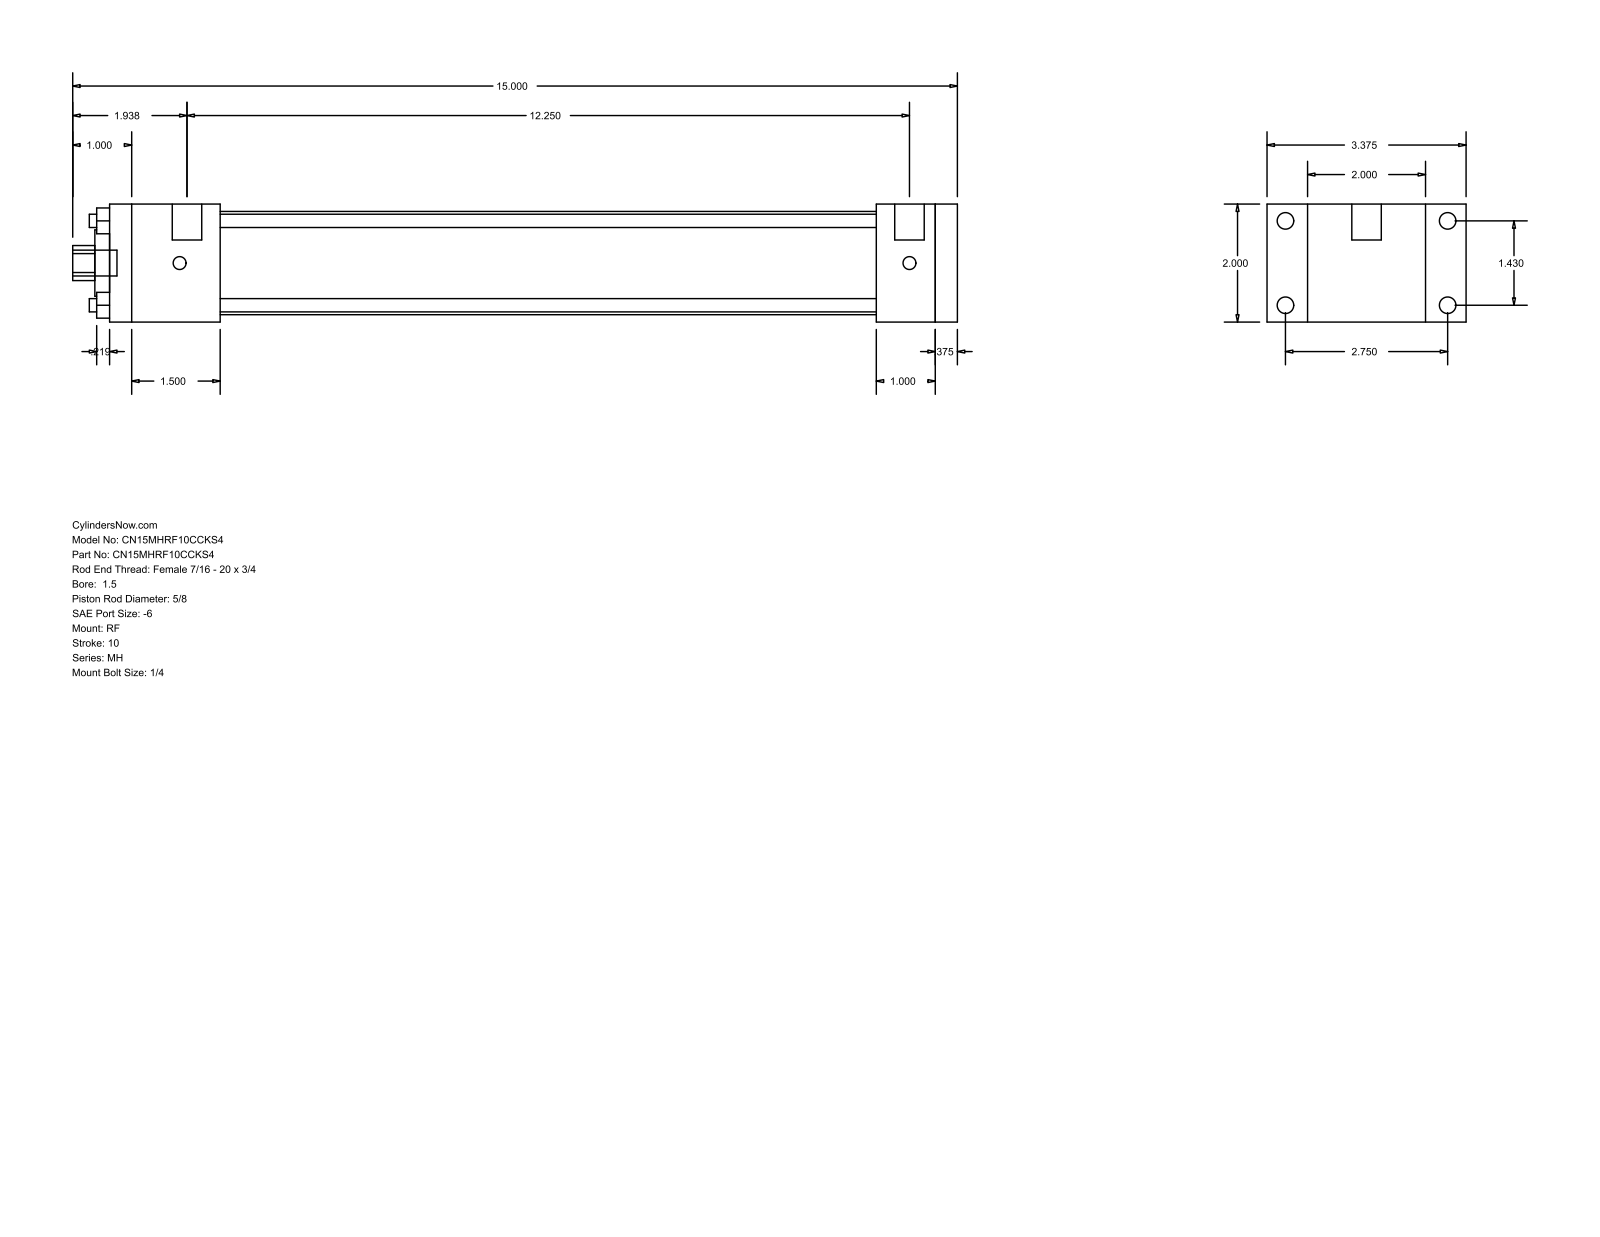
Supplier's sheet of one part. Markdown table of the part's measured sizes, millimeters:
| quantity | value |
| --- | --- |
| part name | MH_RF__0150_0.625 |
| STEP written by | GSSL Pune (CONFIG_CONTROL_DESIGN) |
| units | millimeters |
| bodies | 0 solids, 92 faces (64 planar, 28 cylindrical, 0 other) |
| overall size | 381 × 85.72 × 50.8 |
| round holes (diameter × count) | 5.71 × 4, 15.88 × 1, 28.57 × 1, 44.45 × 1 |
| round bosses / shafts (diameter × count) | 7.14 × 4, 5.56 × 4, 12.7 × 2, 11.11 × 1 |
| partial cylindrical surfaces (radius × count) | 7.54 × 1 |
| main face-to-face distances | 50.8, 9.52, 355.6, 365.12, 17.46, 68.26, 330.19, 25.41, 34.93, 47.62 |
| hole center spacings | 25.68, 36.32, 51.36 |
